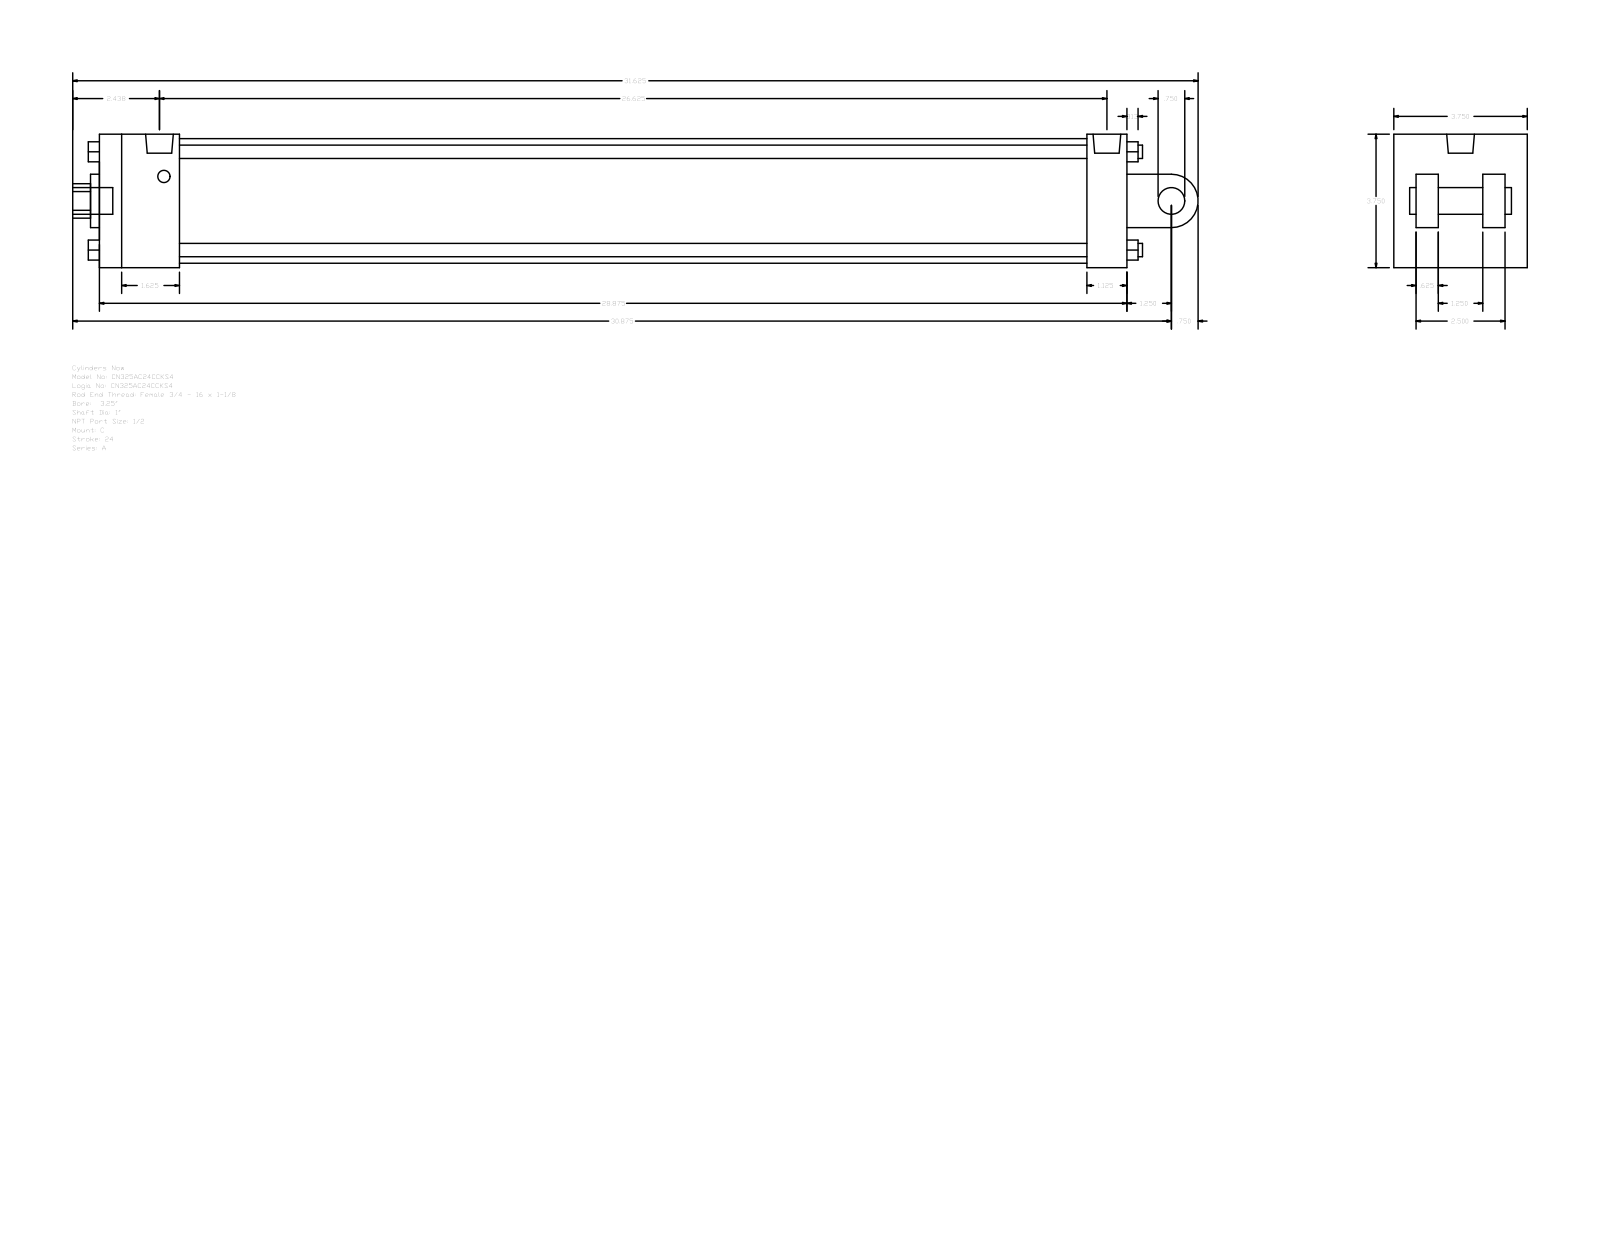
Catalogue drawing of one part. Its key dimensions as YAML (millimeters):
part_name: "A_C__0325_1"
step_written_by: "GSSL Pune (CONFIG_CONTROL_DESIGN)"
units: millimeters
bodies: {solids: 0, faces: 135, planar: 102, cylindrical: 33, other: 0}
overall_size: [803.27, 95.25, 95.25]
round_holes:
  - {diameter: 8.73, count: 2}
  - {diameter: 19.77, count: 1}
  - {diameter: 25.4, count: 1}
  - {diameter: 38.1, count: 1}
  - {diameter: 88.9, count: 1}
round_bosses_or_shafts:
  - {diameter: 9.53, count: 4}
  - {diameter: 19.05, count: 2}
  - {diameter: 8.73, count: 2}
  - {diameter: 19.77, count: 1}
partial_cylinders:
  - {radius: 12.29, count: 1}
  - {radius: 19.05, count: 1}
face_to_face_distances: [95.24, 733.43, 15.87, 63.5, 47.63, 31.74, 79.37, 66.67, 704.85, 28.58]
hole_center_spacings: [3.18]
